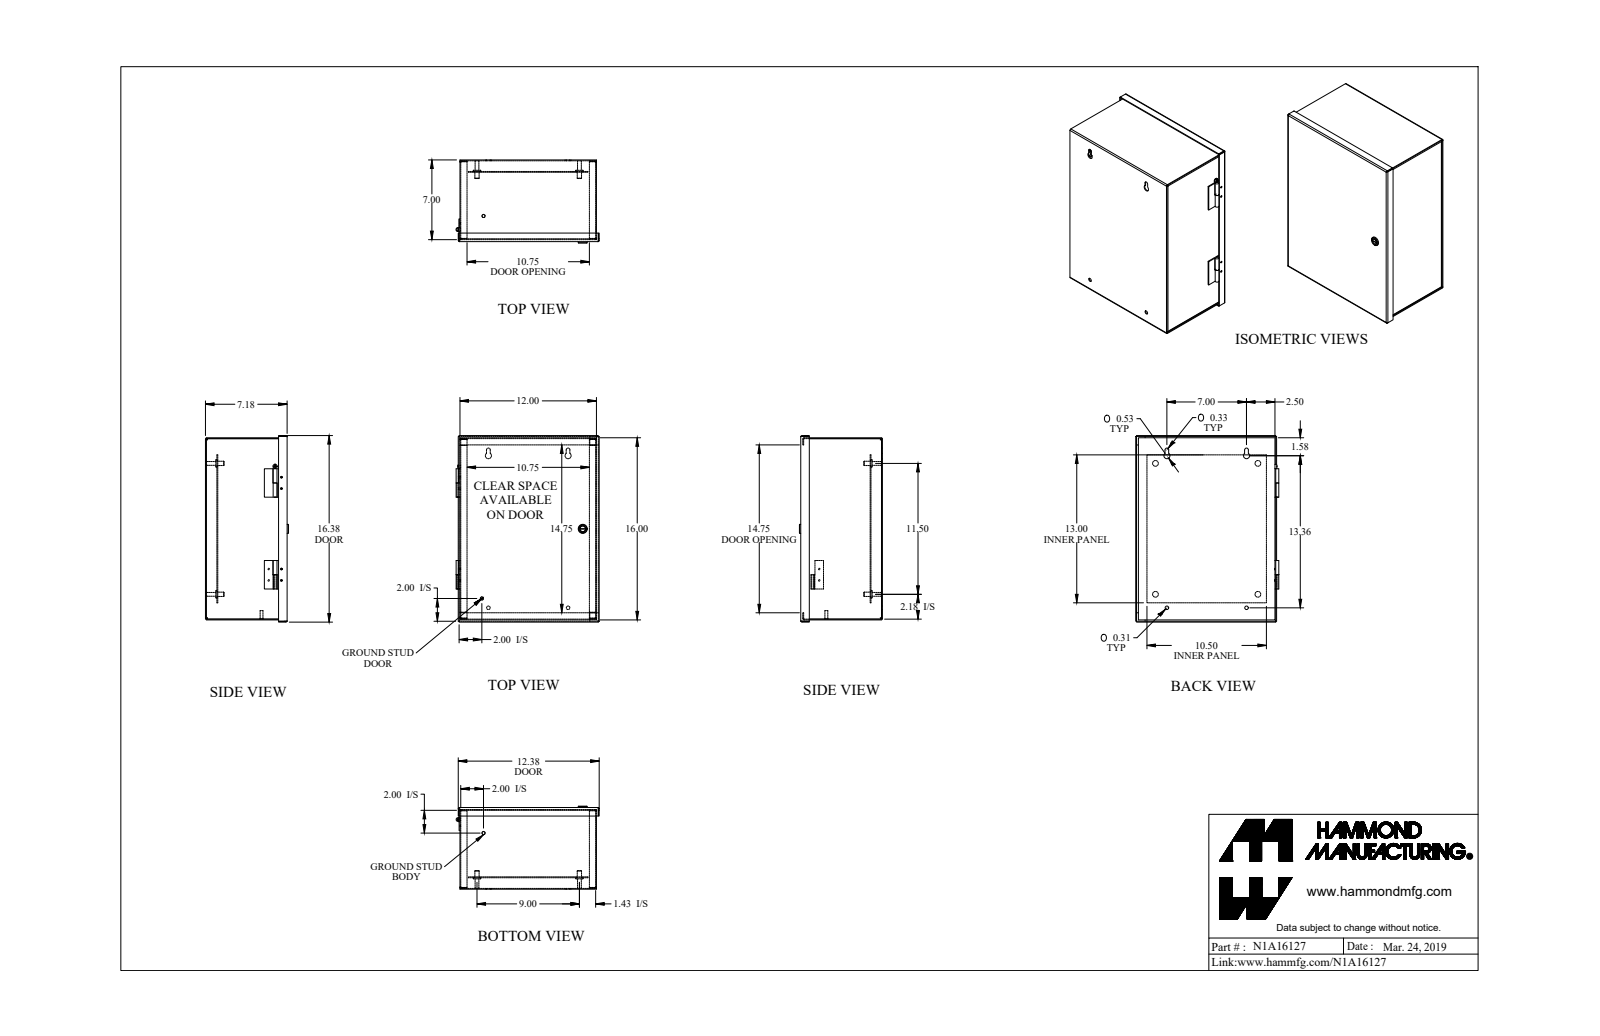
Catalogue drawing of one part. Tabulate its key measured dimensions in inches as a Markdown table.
| quantity | value |
| --- | --- |
| part name | N1A16127 |
| STEP written by | SolidWorks 2018 (AUTOMOTIVE_DESIGN) |
| units | inches |
| bodies | 23 solids, 520 faces (294 planar, 182 cylindrical, 44 other) |
| overall size | 16.384 × 12.574 × 7.299 |
| volume | 75.19 in³ |
| surface area | 2 093 in² |
| round holes (diameter × count) | 0.14 × 8, 0.5 × 4, 0.307 × 2, 0.312 × 2, 0.445 × 2, 0.17 × 1, 0.187 × 1, 0.516 × 1 |
| round bosses / shafts (diameter × count) | 0.128 × 8, 0.375 × 5, 0.65 × 4, 0.33 × 4, 1 × 2, 0.281 × 2, 0.25 × 2, 0.788 × 1 |
| partial cylindrical surfaces (radius × count) | 0.036 × 16, 0.108 × 16, 0.06 × 2, 0.153 × 2, 0.164 × 2, 0.266 × 2, 0.03 × 1, 0.125 × 1 |
| main face-to-face distances | 0.072, 7.105, 1.009, 6.096, 11.928, 7.033, 7.177, 15.928, 1.081, 6.024 |
| hole center spacings | 1, 1.119, 1.104, 1.553, 2.031, 5.757, 8.062, 8.062 |
